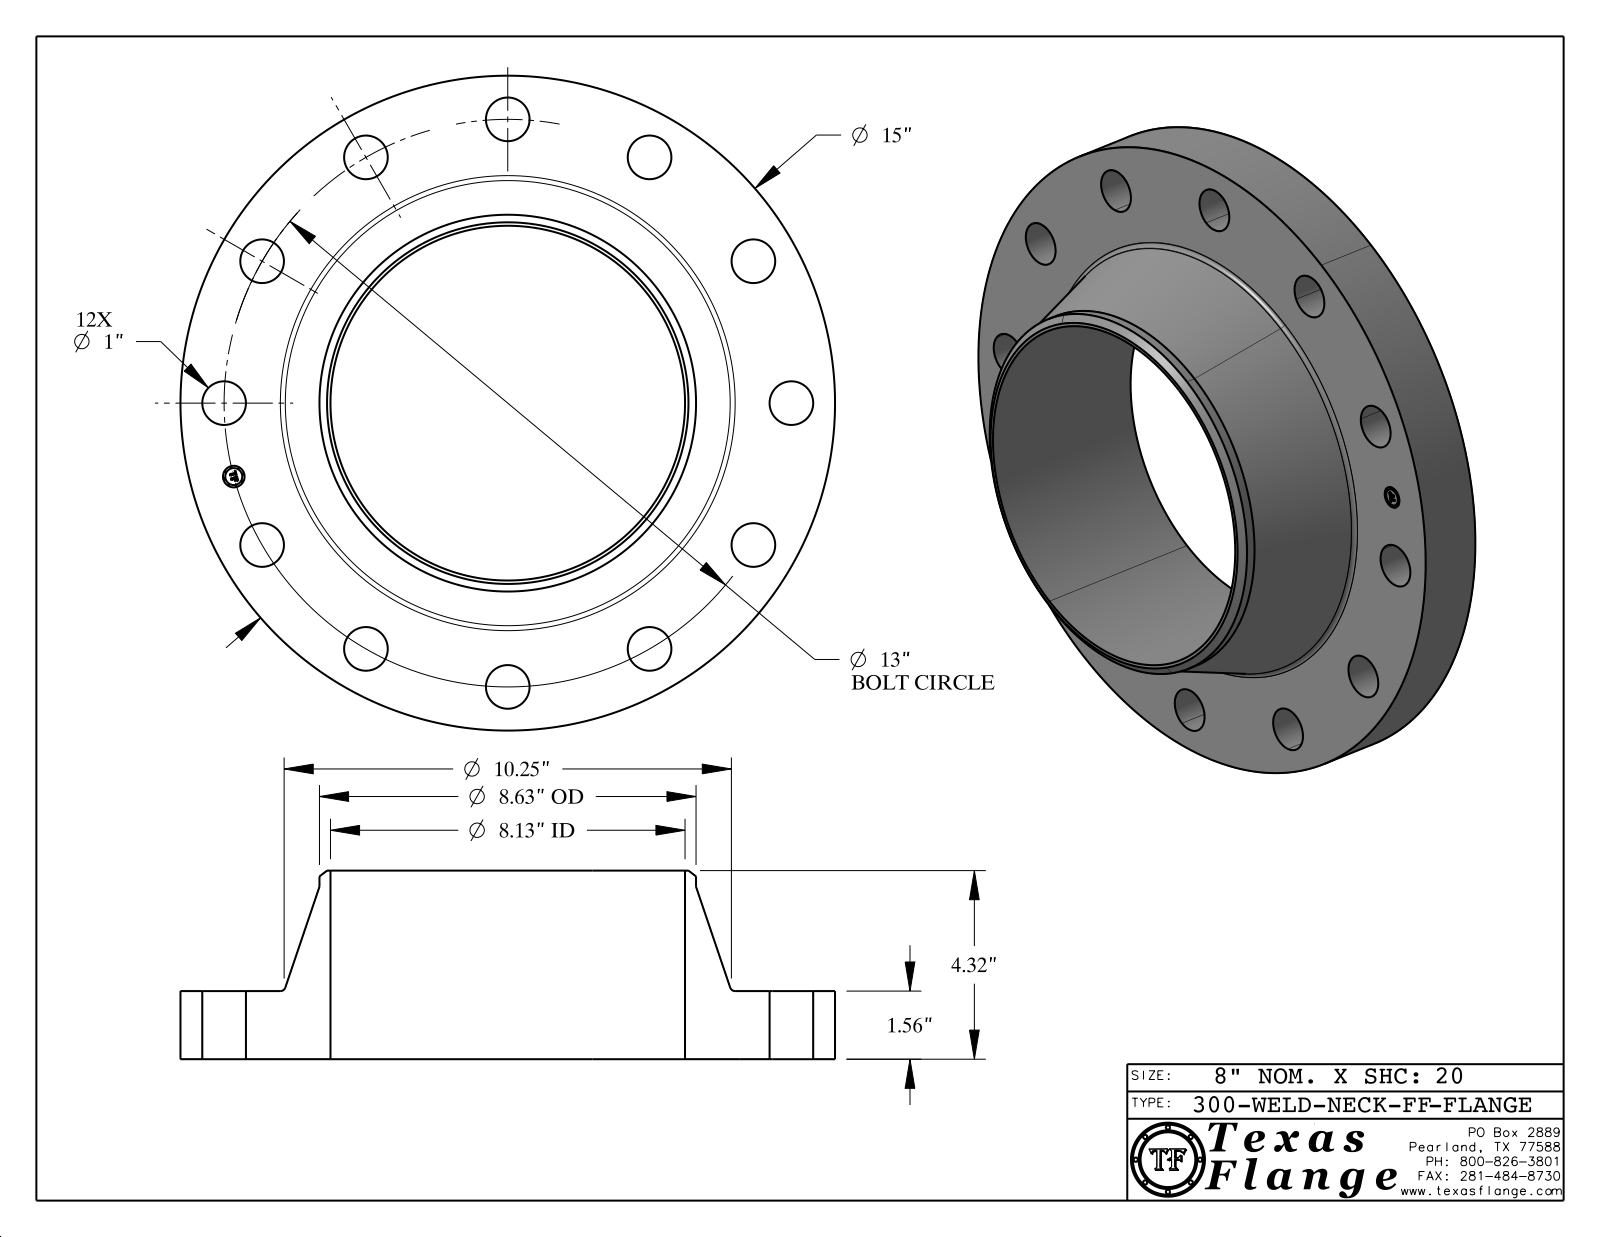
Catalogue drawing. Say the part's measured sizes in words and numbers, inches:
The part is named "300-WELD-NECK-FF". Its 3-D file was written by "CATIA V5 STEP AP214 (AUTOMOTIVE_DESIGN)". It is 1 solid with 425 faces: 369 planar, 50 cylindrical and 6 other. Overall it measures 15 by 15 by 4.32 inches. Its volume is 226.1 cubic inches and its surface area 531.3 square inches. Round holes: 12 of diameter 1, 1 of diameter 0.495, 1 of diameter 8.125. Round bosses or shafts: 8 of diameter 0.03, 1 of diameter 15, 1 of diameter 8.63, 1 of diameter 0.39. The main face-to-face distances are 1.56, 4.32, 2.76, 1.545, 0.015, 2.775, 0.148, 0.144, 0.027, 0.096. The hole center spacings are 6.5, 3.365, 9.193, 11.258, 12.557, 13, 1.697, 4.975.
